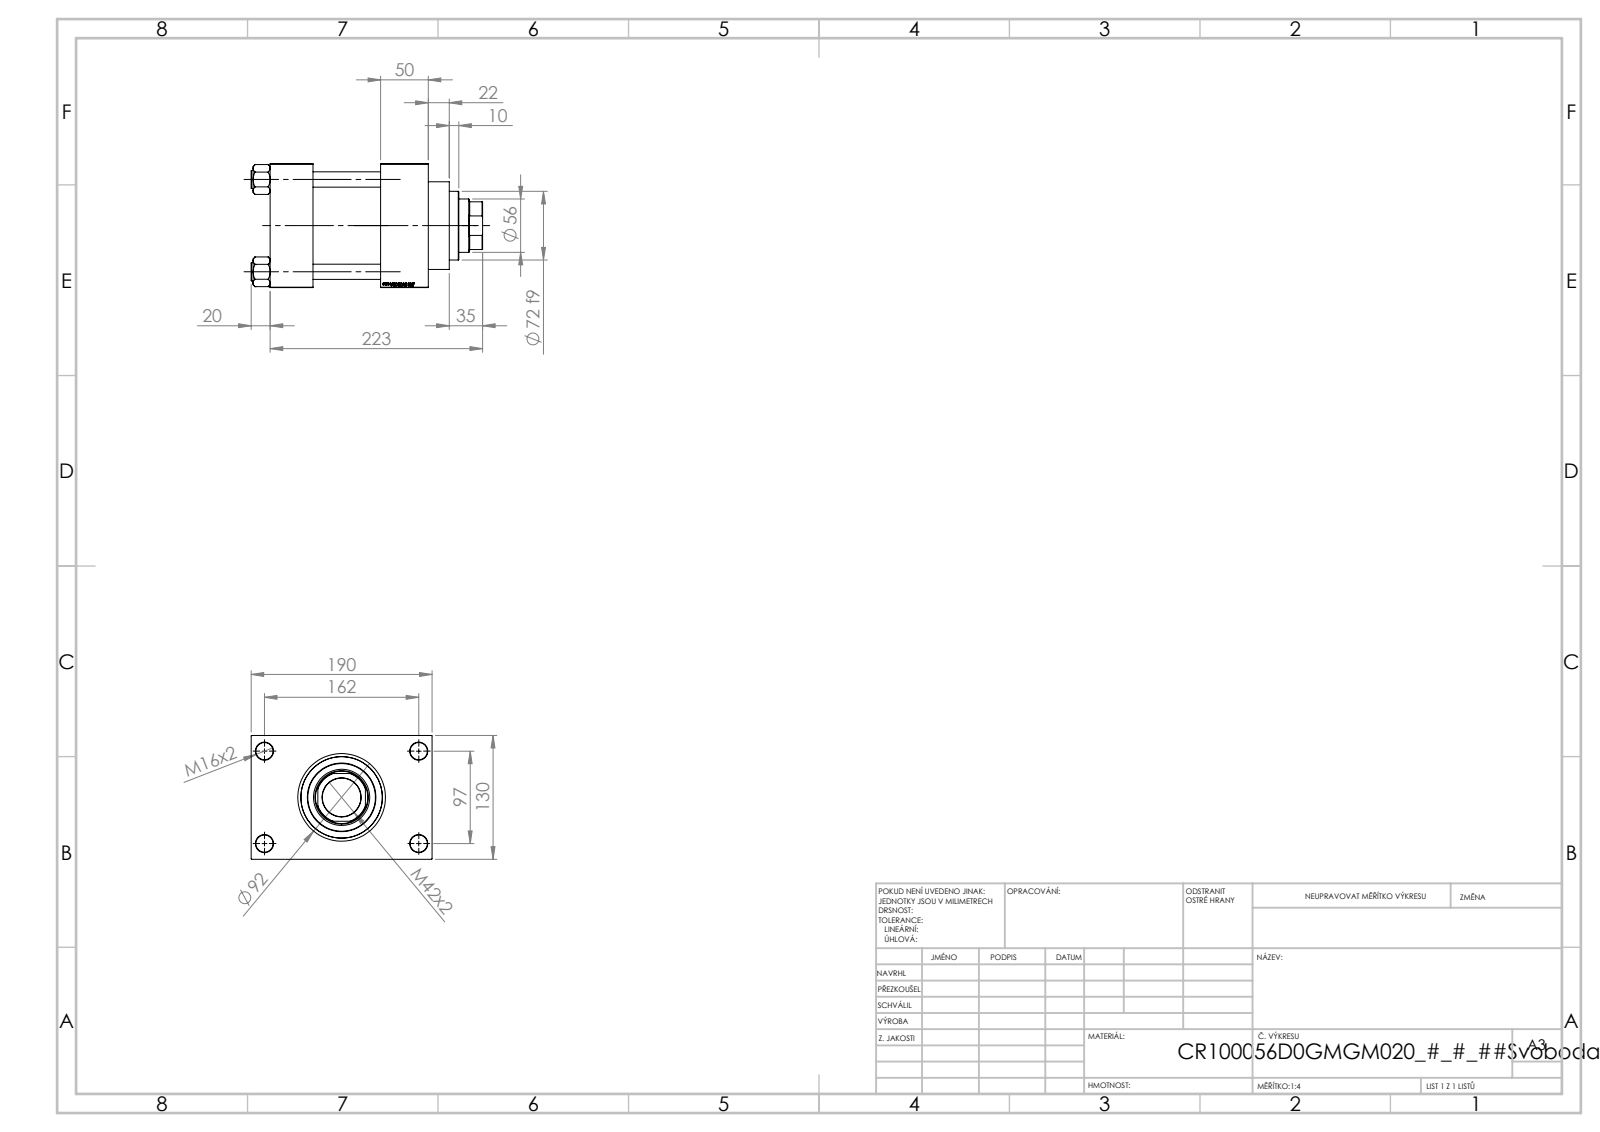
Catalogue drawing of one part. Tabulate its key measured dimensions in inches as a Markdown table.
| quantity | value |
| --- | --- |
| part name | V215CR_D_Body; V215_VC_A; V215CR_VCP_D; NUT_M5_D (+1 more) |
| STEP written by | SolidWorks 2019 (CONFIG_CONTROL_DESIGN) |
| units | inches |
| bodies | 11 solids, 1151 faces (545 planar, 88 cylindrical, 518 other) |
| overall size | 9.567 × 7.48 × 5.118 |
| volume | 160.4 in³ |
| surface area | 561.4 in² |
| round holes (diameter × count) | 0.63 × 4, 0.709 × 4, 0.276 × 2, 1.041 × 2, 1.378 × 2, 1.594 × 1, 2.205 × 1, 2.323 × 1, 2.992 × 1, 3.366 × 1, 3.937 × 1 |
| round bosses / shafts (diameter × count) | 0.748 × 4, 4.173 × 1, 3.622 × 1, 2.835 × 1 |
| partial cylindrical surfaces (radius × count) | 1.063 × 1 |
| main face-to-face distances | 5.118, 4.567, 1.969, 1.772, 2.795, 4.764, 6.535, 1.181, 6.299, 0.787 |
| hole center spacings | 1.281, 2.698, 3.717, 3.815, 4.026, 5.096, 6.367, 3.819 |
